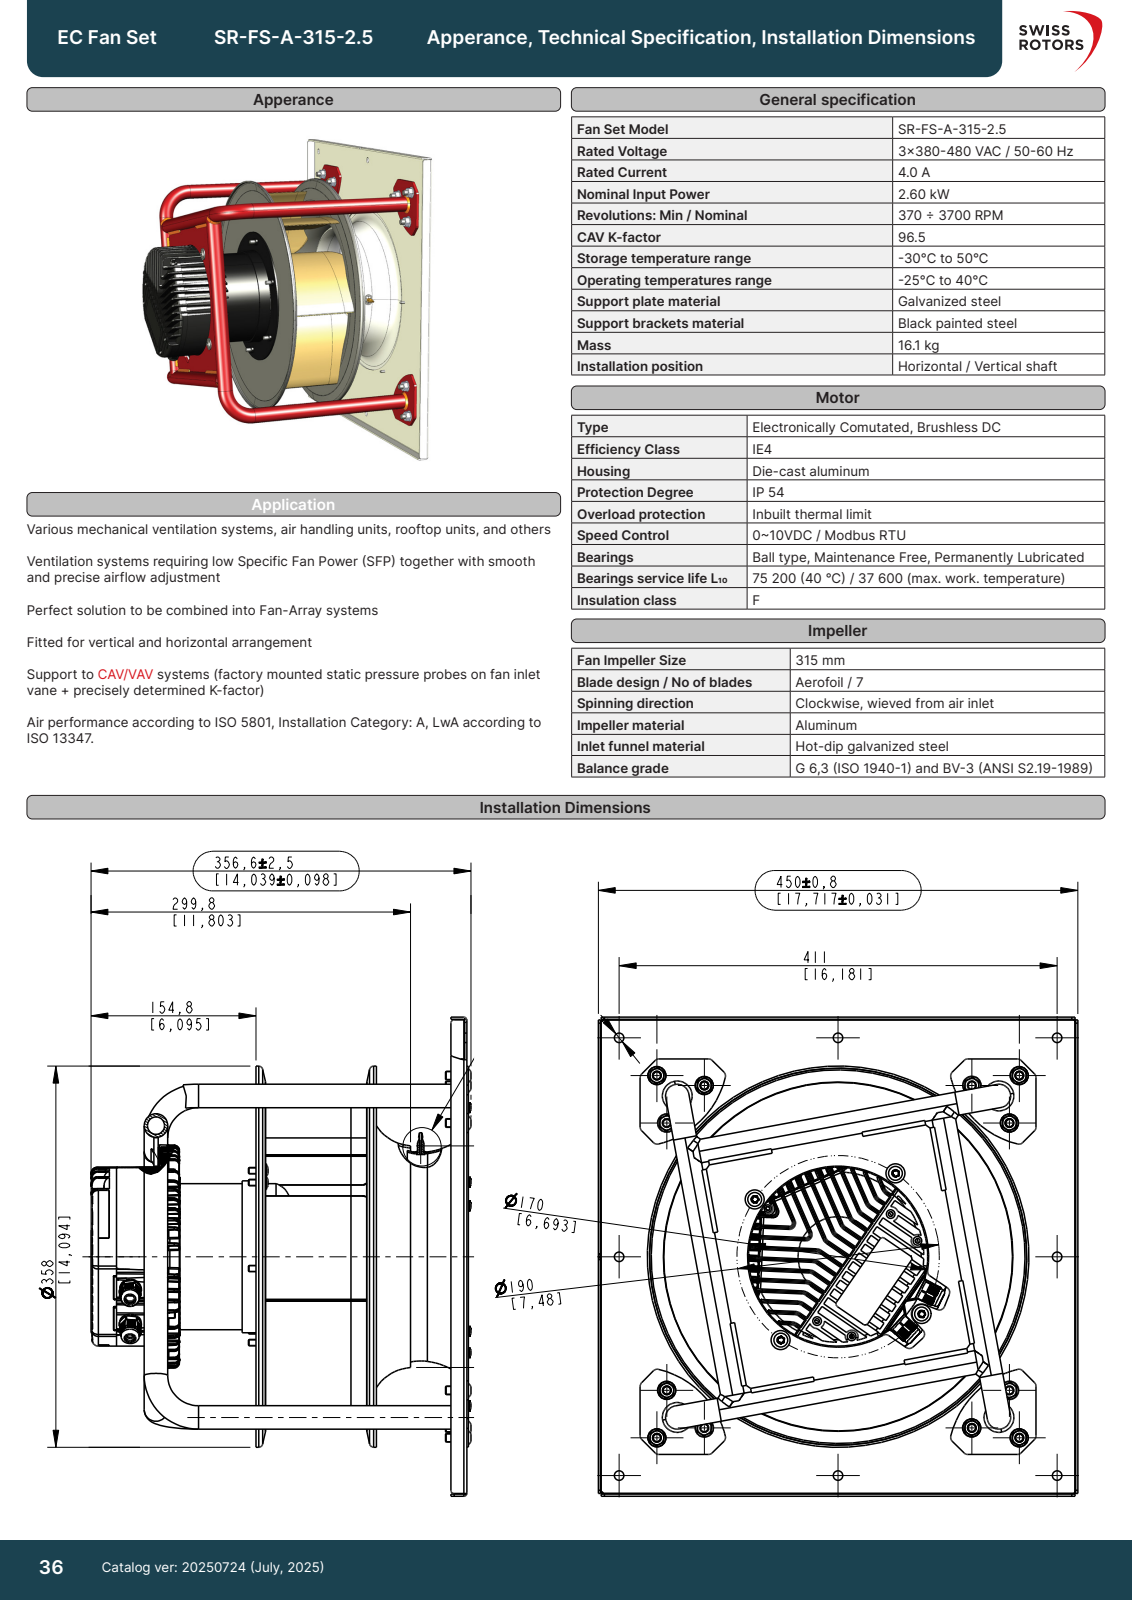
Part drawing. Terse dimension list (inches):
name: 1167311; 1167312; 1167310_ASM; 1195866 (+8 more)
written by: CREO PARAMETRIC BY PTC INC, 2022484 (CONFIG_CONTROL_DESIGN)
unit: in
bodies: 42 solids, 15933 faces (4049 planar, 5759 cylindrical, 6125 other)
size: 17.717 × 17.717 × 13.724
volume: 692 in³; area: 3 291 in²
holes: 8× ⌀0.098, 8× ⌀0.354, 8× ⌀0.551, 7× ⌀0.177, 6× ⌀0.122, 6× ⌀0.197, 6× ⌀0.252, 6× ⌀0.339, 6× ⌀0.346, 5× ⌀0.193, 4× ⌀0.157, 4× ⌀0.256
bosses: 24× ⌀0.098, 12× ⌀0.236, 8× ⌀0.697, 8× ⌀0.197, 6× ⌀0.512, 6× ⌀0.433, 6× ⌀0.354, 6× ⌀0.157
rounds: 1100× R0.039, 388× R0.02, 366× R0.024, 325× R0.012, 176× R0.059, 163× R0.028, 144× R0.335, 108× R0.167
face distances: 0.079, 7.437, 7.516, 3.89, 11.327, 11.406, 0.118, 4.008, 11.445, 11.524
hole spacings: 3.445, 5.967, 3.445, 6.89, 3.444, 5.967, 6.327, 6.89
